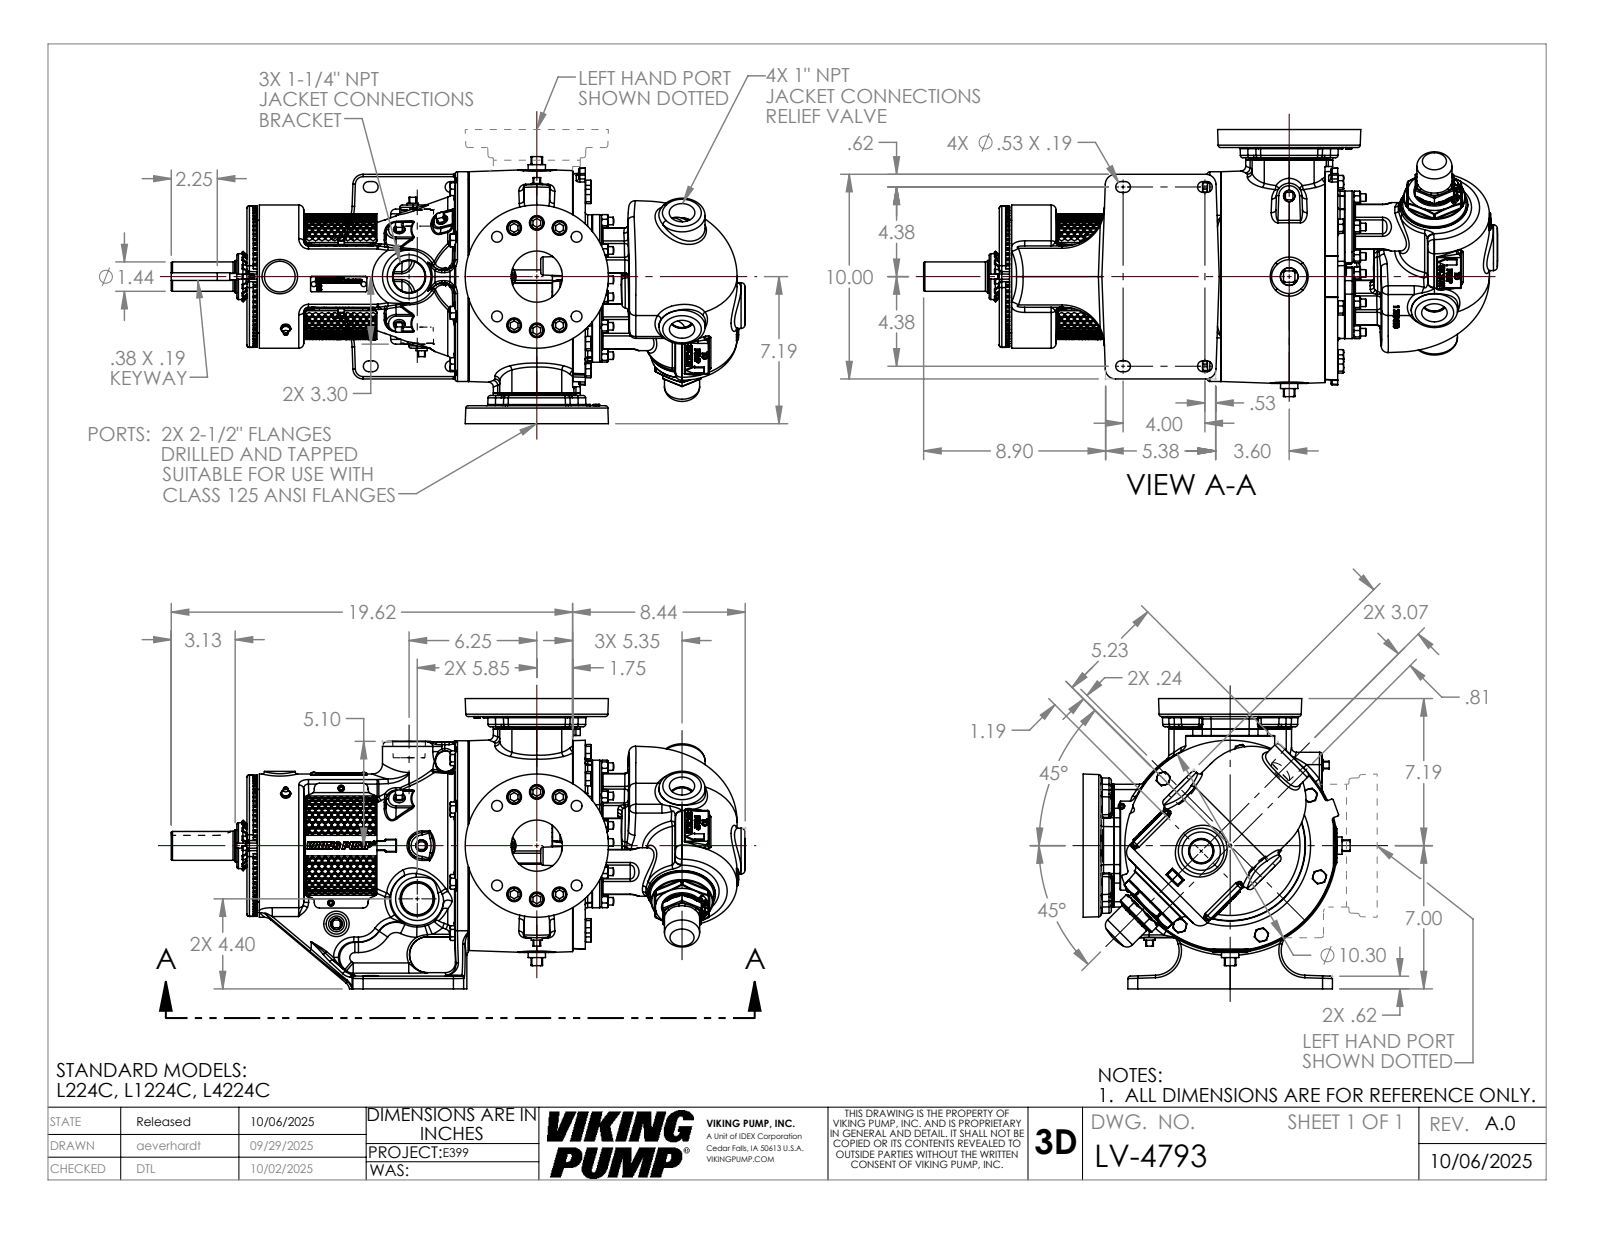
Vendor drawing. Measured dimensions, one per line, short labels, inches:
name: LV-4793
written by: SolidWorks 2024 (AUTOMOTIVE_DESIGN)
unit: in
bodies: 1 solid, 6330 faces (1854 planar, 1037 cylindrical, 3439 other)
size: 28.059 × 14.188 × 13.053
volume: 1 214 in³; area: 1 592 in²
holes: 12× ⌀0.719, 8× ⌀0.531, 8× ⌀1.094, 6× ⌀0.199, 6× ⌀0.25, 3× ⌀0.159, 2× ⌀0.266, 2× ⌀0.313, 2× ⌀2.5, 1× ⌀0.453, 1× ⌀1.577, 1× ⌀1.593
bosses: 12× ⌀0.66, 9× ⌀0.625, 8× ⌀0.369, 6× ⌀0.625, 3× ⌀3.5, 3× ⌀0.437, 3× ⌀0.312, 1× ⌀10.25
rounds: 109× R0.063, 82× R0.12, 74× R0.069, 34× R0.01, 34× R0.03, 34× R0.5, 28× R0.009, 16× R0.06
face distances: 14.187, 0.5, 2.25, 13.792, 3.537, 10.255, 2.75, 0.88, 0.62, 2.143
hole spacings: 3, 2.75, 2.625, 1.375, 0.941, 1.136, 2.06, 2.18
